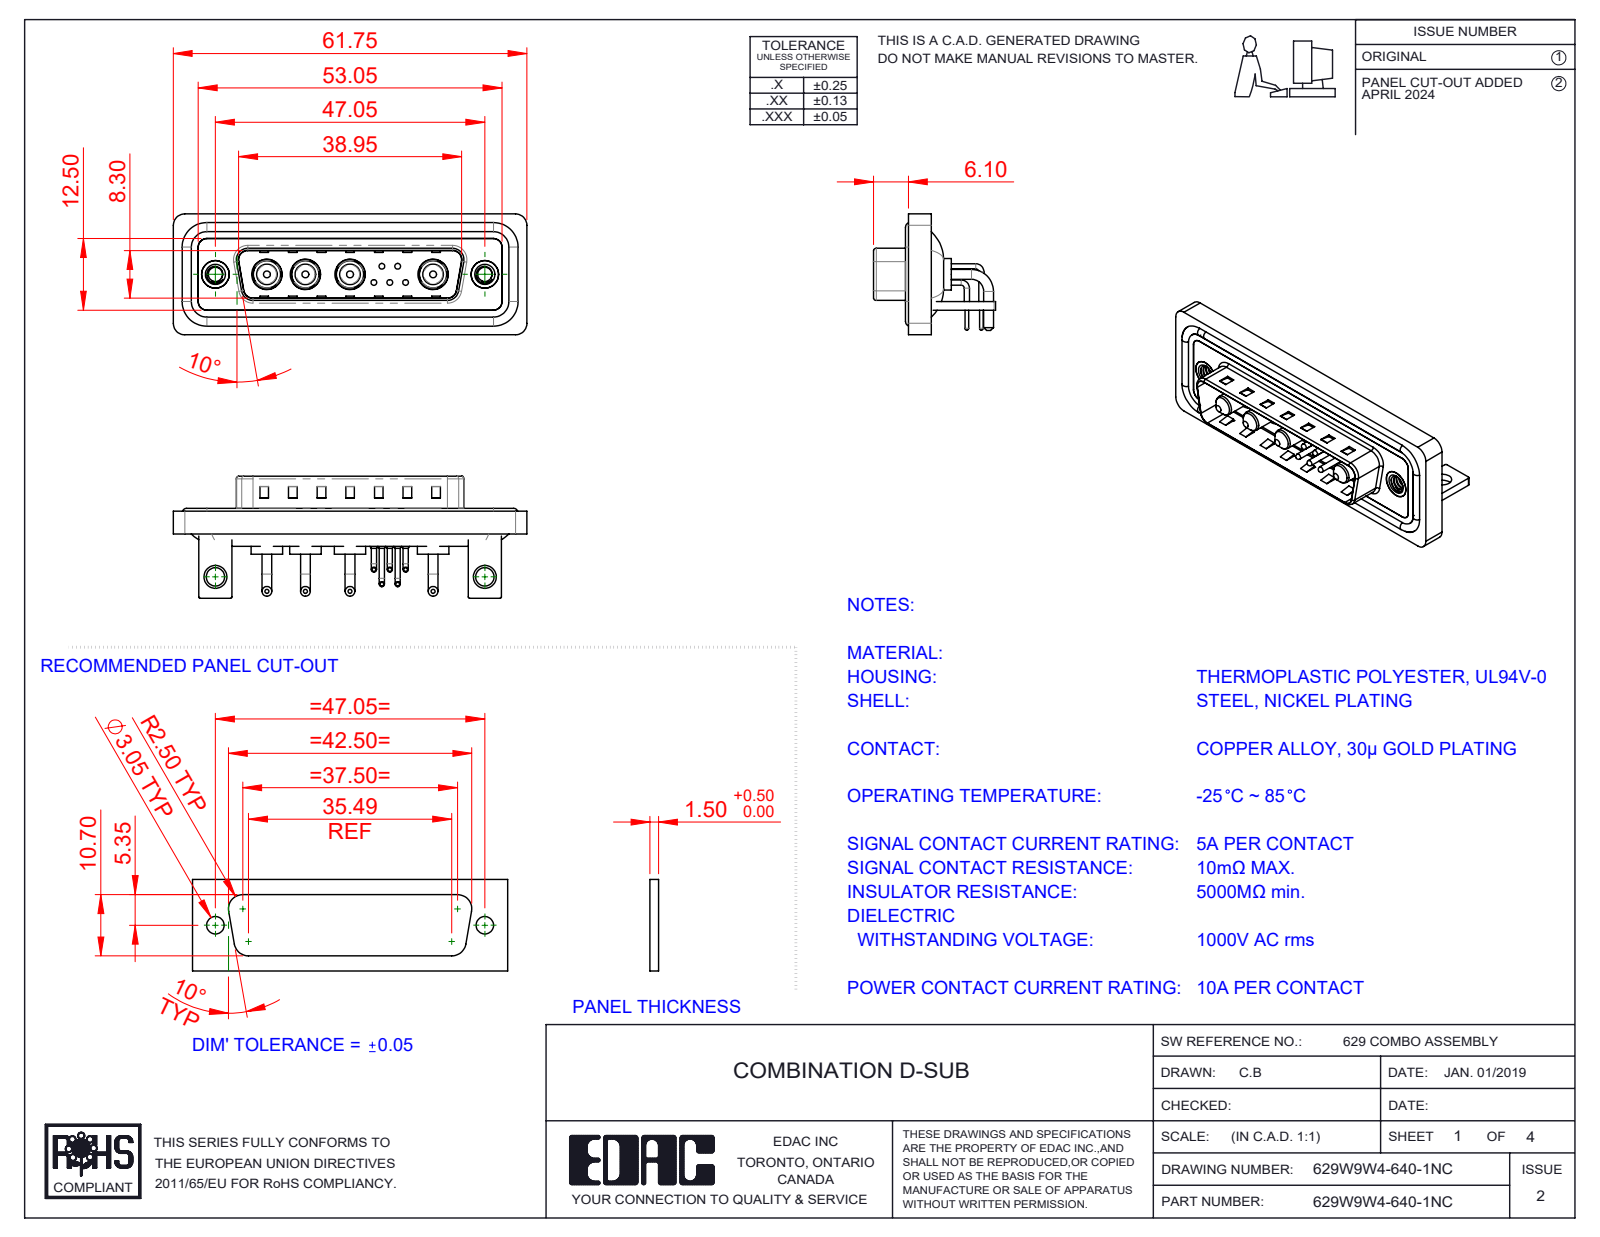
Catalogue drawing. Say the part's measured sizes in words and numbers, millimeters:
The part is named "629Combo Threaded Rivet_B; 629Combo Housing_9W4; 629Combo Contact Row 2; 629W9W4-640-1NC (+6 more)". Its 3-D file was written by "SolidWorks 2023 (CONFIG_CONTROL_DESIGN)". It is 22 solids with 1243 faces: 589 planar, 470 cylindrical and 184 other. Overall it measures 61.75 by 21.3 by 21.1 millimeters. Its volume is 7 744 cubic millimeters and its surface area 12 761 square millimeters. Round holes: 5 of diameter 0.75, 5 of diameter 1.6, 5 of diameter 2, 4 of diameter 4.85, 4 of diameter 5.3, 2 of diameter 2.5, 2 of diameter 3.2, 2 of diameter 4, 2 of diameter 4.8, 2 of diameter 5. Round bosses or shafts: 10 of diameter 0.9, 8 of diameter 1.7, 5 of diameter 1.5, 5 of diameter 1, 5 of diameter 0.65, 4 of diameter 5.5, 4 of diameter 5.2, 4 of diameter 4.75. Partial cylindrical surfaces (rounded edges, fillets, slot ends): 19 of radius 2, 18 of radius 1.5, 16 of radius 0.25, 9 of radius 0.5, 8 of radius 1.6, 5 of radius 1.01, 4 of radius 0.6, 4 of radius 0.65. The main face-to-face distances are 0.4, 1.5, 0.8, 2.9, 2.1, 1.1, 3.7, 4.1, 4.5, 1.6. The hole center spacings are 3.16, 2.77, 5.04, 14.5, 47.05, 2.78, 4.4, 4.41.
